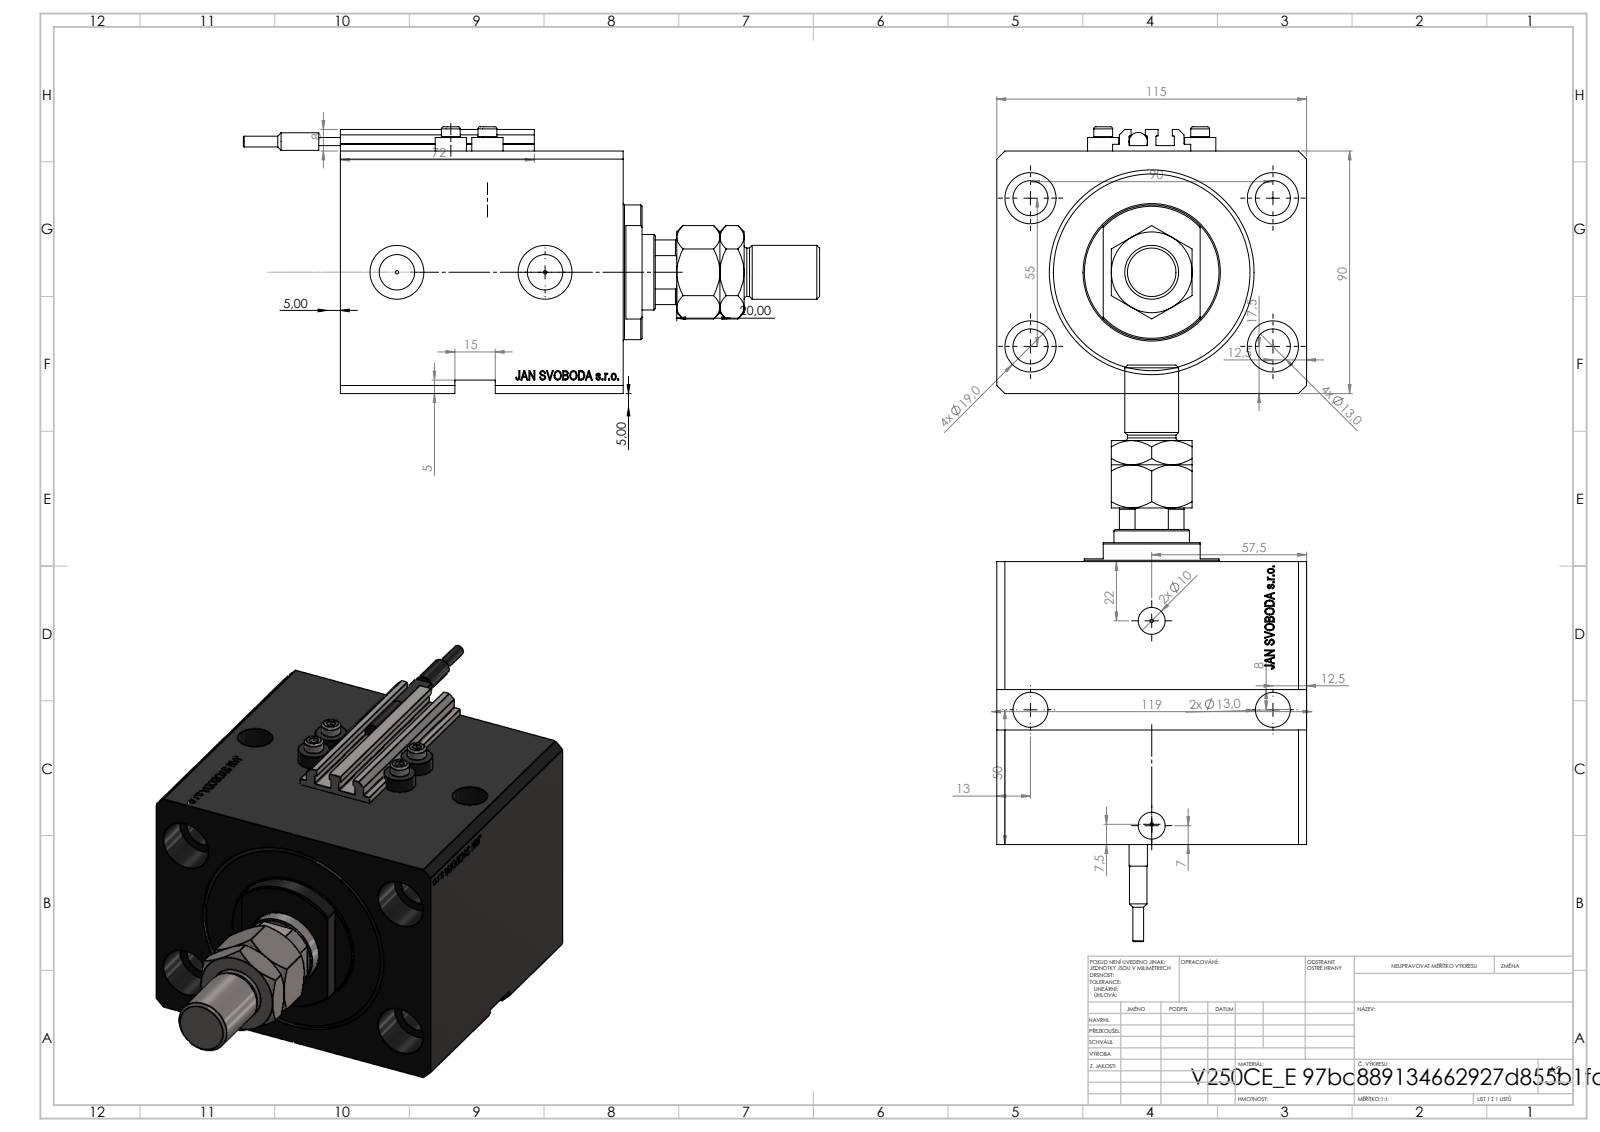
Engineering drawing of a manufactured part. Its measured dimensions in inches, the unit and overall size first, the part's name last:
Units: inches
Overall size (bounding box): 8.421 × 4.528 × 3.898
Round holes (diameter × count): ⌀0.512 ×6, ⌀0.049 ×4, ⌀0.157 ×4, ⌀0.748 ×4, ⌀0.394 ×2, ⌀0.518 ×2, ⌀0.787 ×2, ⌀0.728 ×1, ⌀1.102 ×1, ⌀2.48 ×1, ⌀2.992 ×1
Round bosses / shafts (diameter × count): ⌀0.457 ×4, ⌀0.276 ×4, ⌀1.969 ×1, ⌀0.787 ×1, ⌀0.709 ×1, ⌀0.268 ×1, ⌀0.256 ×1, ⌀0.157 ×1
Partial cylindrical surfaces — rounded edges, fillets, slot ends (radius × count): R0.008 ×10, R0.531 ×1
Main face-to-face distances: 3.543, 4.528, 4.134, 3.429, 0.705, 2.244, 2.949, 1.185, 0.787, 2.161
Hole centre spacings: 2.076, 2.165, 3.543, 0.535, 1.078, 1.12, 1.324, 1.417
Volume: 60.06 in³ · Surface area: 253.8 in²
Bodies: 10 solids, 1182 faces (574 planar, 136 cylindrical, 472 other)
Part name (STEP PRODUCT): V250CE_C_VCP; V250CE_E; MTA; V250CE_VC_E (+2 more)
STEP written by: SolidWorks 2019 (CONFIG_CONTROL_DESIGN)
